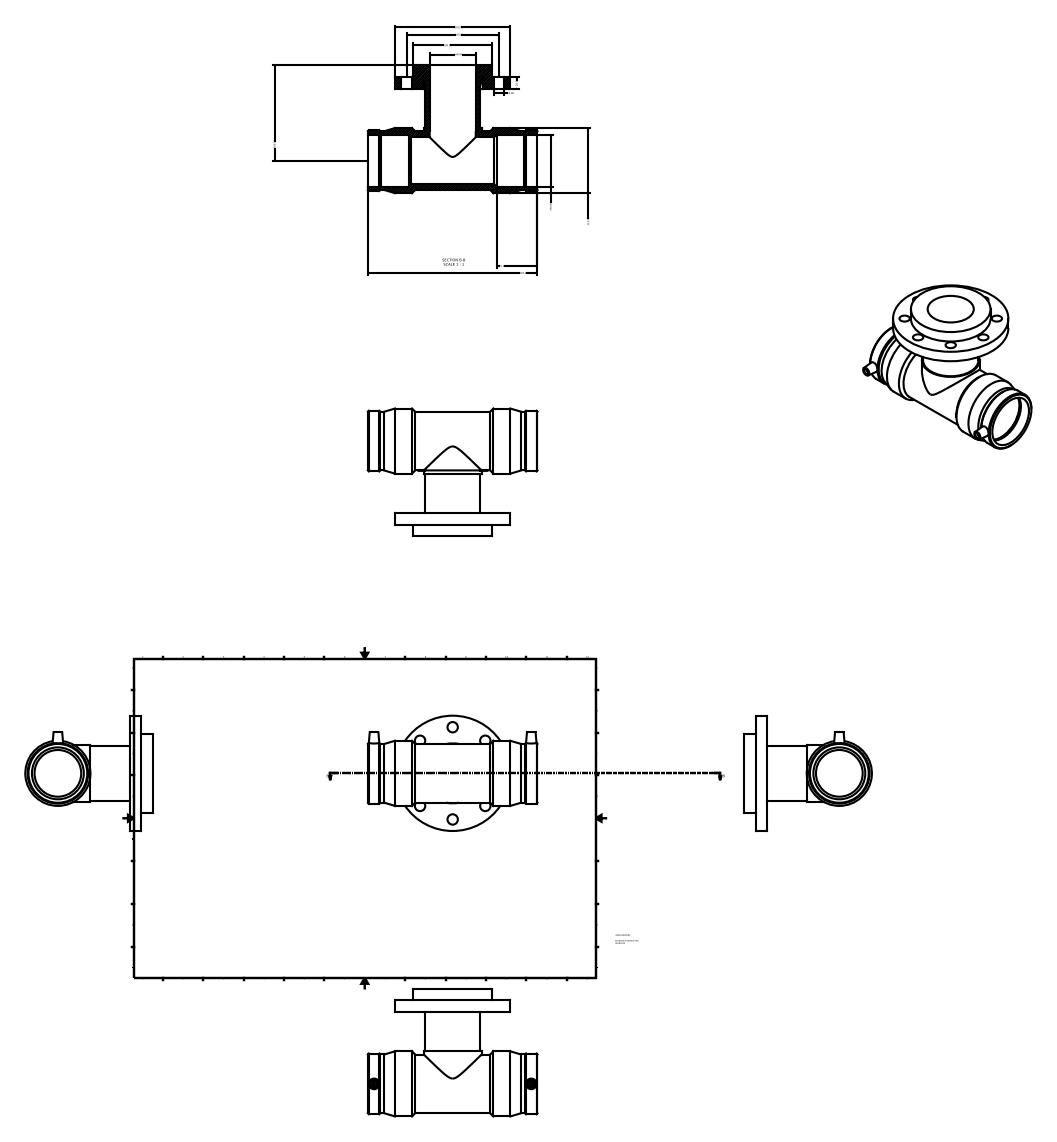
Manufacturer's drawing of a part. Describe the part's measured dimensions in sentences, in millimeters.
The part is named "499404090080". Its 3-D file was written by "Autodesk Inventor 2015 (AUTOMOTIVE_DESIGN)". It is 1 solid with 64 faces: 14 planar, 34 cylindrical and 16 other. Overall it measures 294 by 221.5 by 200 millimeters. Its volume is 1 696 000 cubic millimeters and its surface area 322 939 square millimeters. Round holes: 8 of diameter 18, 2 of diameter 10, 1 of diameter 80, 1 of diameter 81, 1 of diameter 90, 1 of diameter 104, 1 of diameter 105.09. Round bosses or shafts: 2 of diameter 4, 1 of diameter 200, 1 of diameter 138, 1 of diameter 113, 1 of diameter 101.94, 1 of diameter 101.7, 1 of diameter 100, 1 of diameter 96. The main face-to-face distances are 20, 40, 294, 108.5, 88.5, 68.5, 23.25, 270.75, 247.5, 14. The hole center spacings are 61.23, 80, 113.14, 147.82, 160, 272.7.
